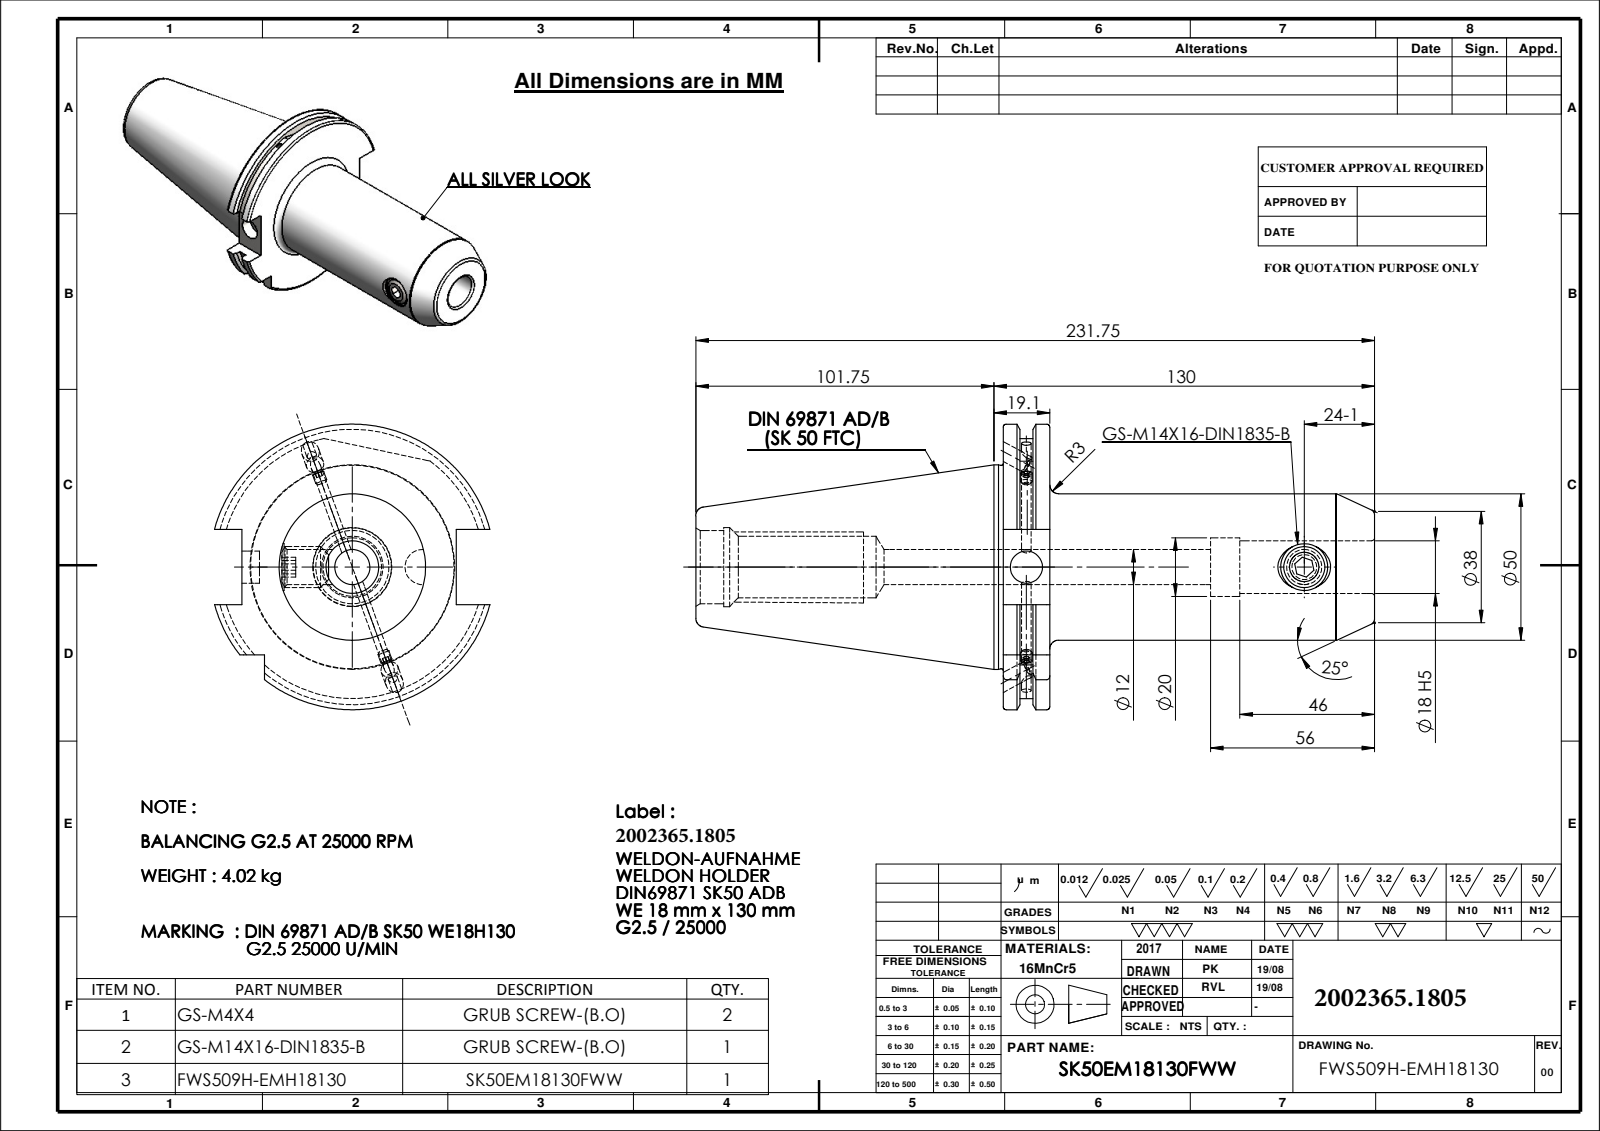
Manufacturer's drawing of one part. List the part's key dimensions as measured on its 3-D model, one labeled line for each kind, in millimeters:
Part name (STEP PRODUCT): M14X16_ISO 4026 - M12 x 12-N; SK50EM18130FWW; Copy of M4X4_DIN 913 - M4 x 4-N; 91506-WE718130
STEP written by: SolidWorks 2009 (CONFIG_CONTROL_DESIGN)
Units: millimetres
Bodies: 4 solids, 168 faces (53 planar, 55 cylindrical, 60 other)
Overall size (bounding box): 231.75 × 97.5 × 94.05
Volume: 522 261 mm³ · Surface area: 66 993 mm²
Round holes (diameter × count): ⌀6 ×2, ⌀12 ×2, ⌀3.3 ×1, ⌀11 ×1, ⌀16 ×1, ⌀18 ×1, ⌀20 ×1, ⌀21 ×1, ⌀25 ×1, ⌀27 ×1
Round bosses / shafts (diameter × count): ⌀4 ×2, ⌀69.85 ×1, ⌀69.45 ×1, ⌀50 ×1, ⌀14 ×1
Partial cylindrical surfaces — rounded edges, fillets, slot ends (radius × count): R44.9 ×1, R48.75 ×1
Main face-to-face distances: 15.9, 126.8, 110.9, 5.66, 10.24, 121.14, 10.15, 4.49, 5.75, 116.65
Hole centre spacings: 94.9
